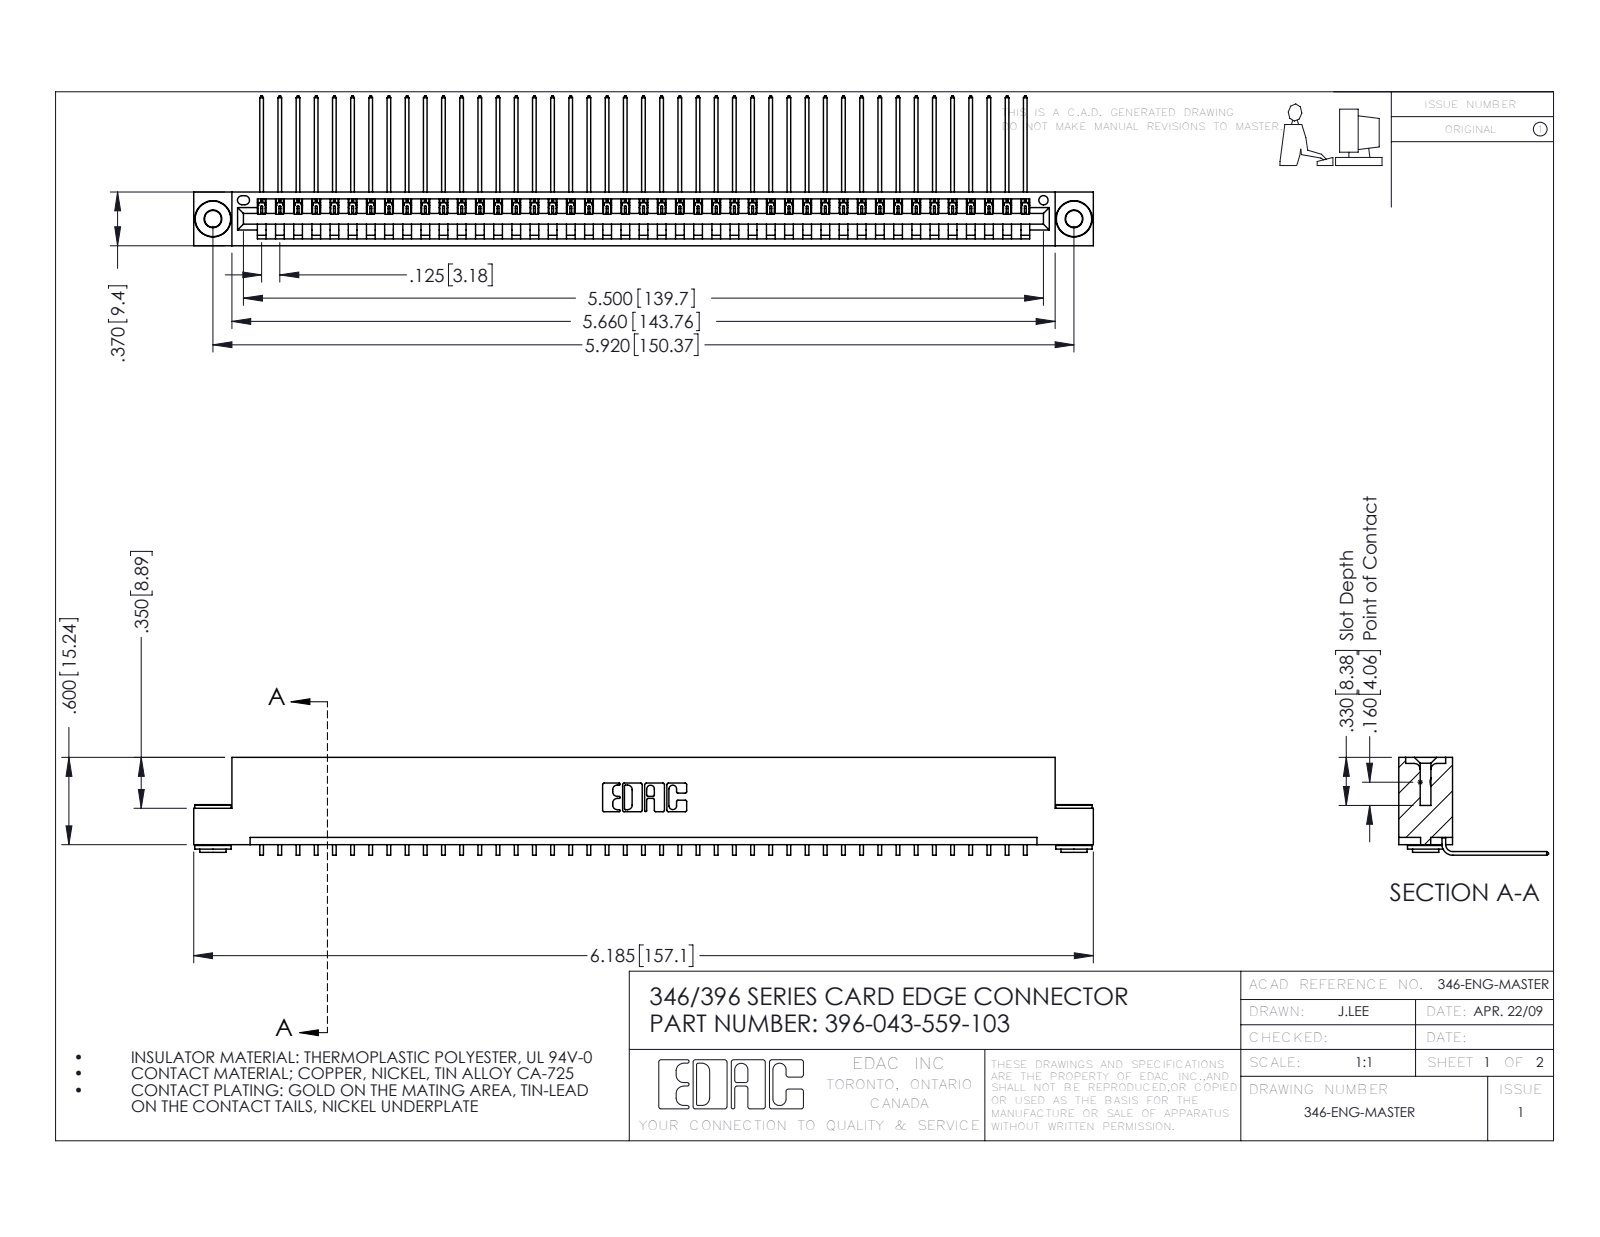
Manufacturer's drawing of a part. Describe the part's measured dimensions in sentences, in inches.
The part is named "345-250-002_345-250-002-102; 396-043-559-103; 345-292-001_558 559 Tail - 1; 346 Part_Flush Mounting Lugs - 0.156 Dia-TH". Its 3-D file was written by "SolidWorks 2016 (CONFIG_CONTROL_DESIGN)". It is 46 solids with 2740 faces: 1892 planar, 840 cylindrical and 8 other. Overall it measures 6.185 by 1.03 by 0.673 inches. Its volume is 0.928 cubic inches and its surface area 31.14 square inches. Round holes: 2 of diameter 0.116, 2 of diameter 0.156, 1 of diameter 0.064. Round bosses or shafts: 2 of diameter 0.25, 2 of diameter 0.18, 2 of diameter 0.136. Partial cylindrical surfaces (rounded edges, fillets, slot ends): 86 of radius 0.006, 22 of radius 0.01, 6 of radius 0.007, 6 of radius 0.031, 3 of radius 0.026, 2 of radius 0.031, 2 of radius 0.04, 1 of radius 0.014. The main face-to-face distances are 0.048, 0.322, 0.37, 0.25, 0.025, 0.072, 0.298, 0.148, 0.222, 0.1. The hole center spacings are 0.246, 5.711, 5.92.
